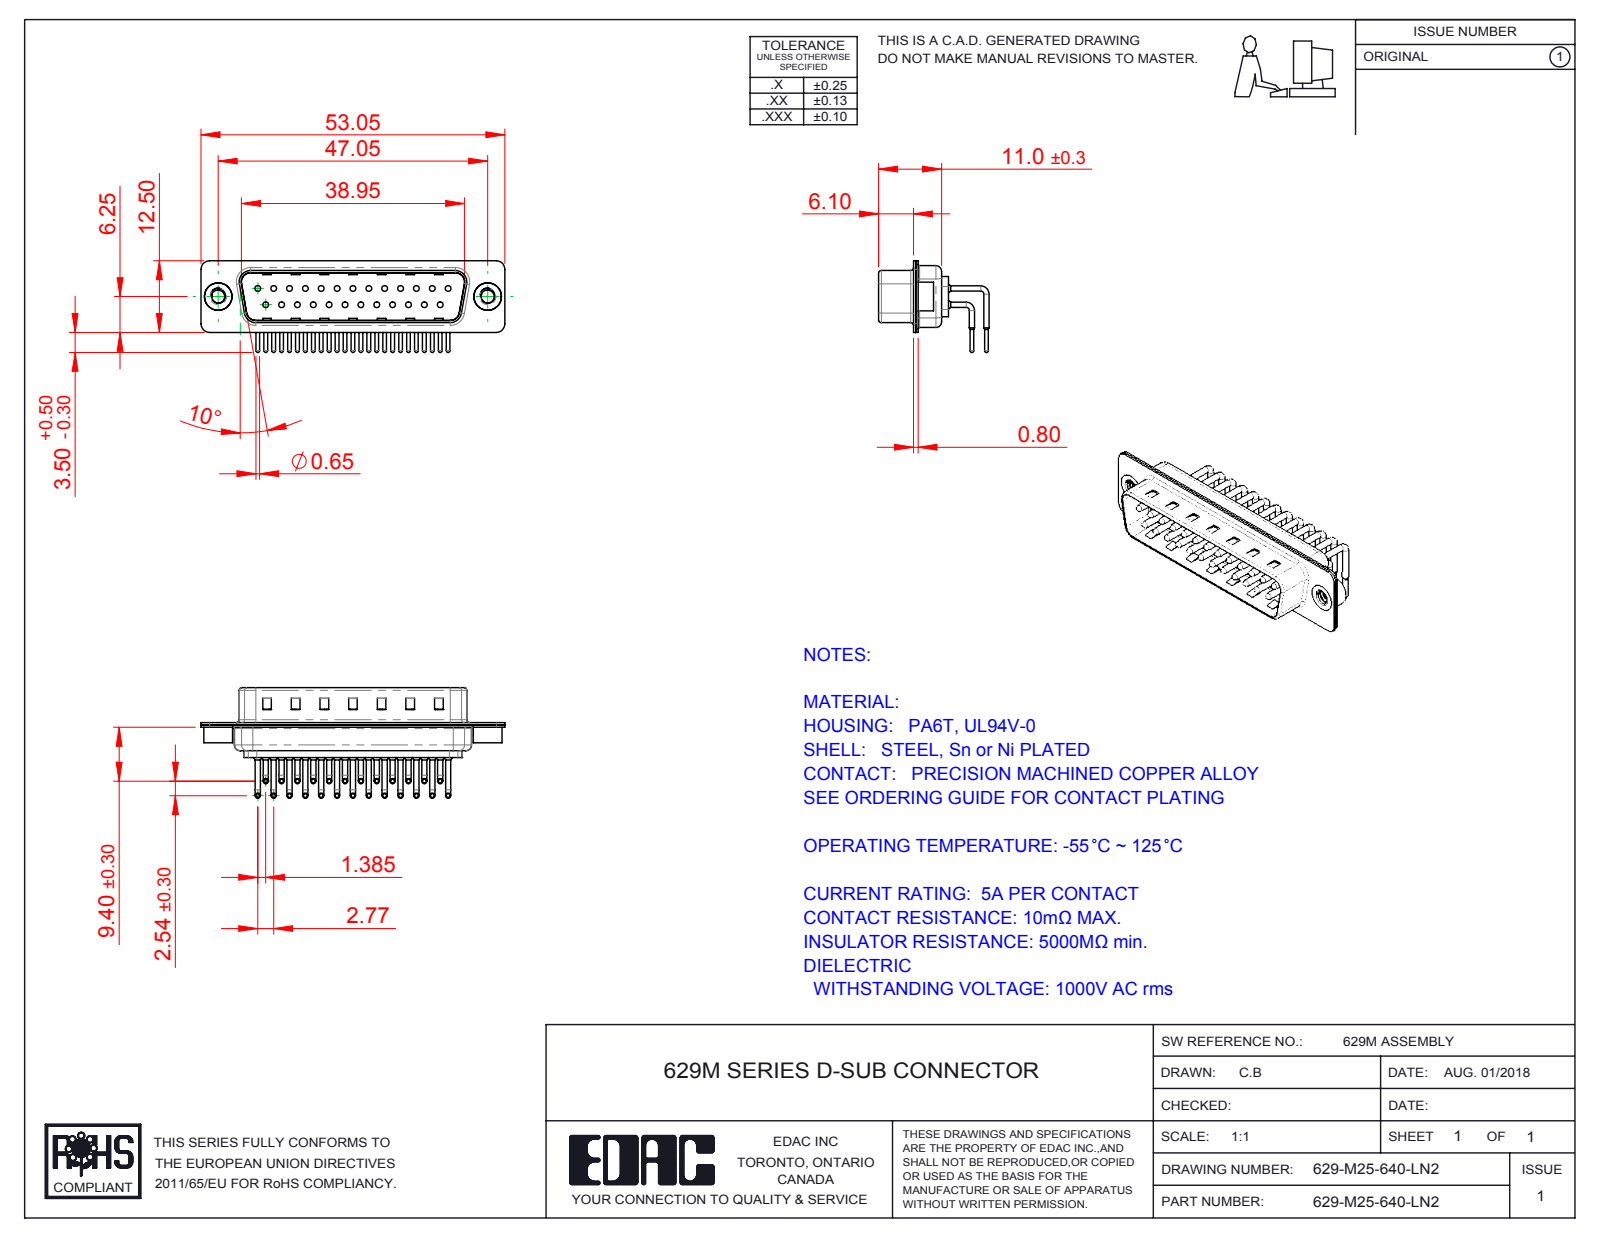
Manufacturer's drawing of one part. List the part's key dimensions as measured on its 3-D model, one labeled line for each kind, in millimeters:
Part name (STEP PRODUCT): 629M Contact Row 1; 629-M25-640-LN2; 629M Shell Front_25 Contacts; 629M 4-40 Threaded Rivet (+3 more)
STEP written by: SolidWorks 2016 (CONFIG_CONTROL_DESIGN)
Units: millimetres
Bodies: 30 solids, 3126 faces (1771 planar, 1037 cylindrical, 318 other)
Overall size (bounding box): 53.05 × 19.29 × 16
Volume: 2 911 mm³ · Surface area: 7 760 mm²
Round holes (diameter × count): ⌀1 ×25, ⌀1.7 ×25, ⌀2 ×25, ⌀2.26 ×2, ⌀4 ×2, ⌀4.8 ×2
Round bosses / shafts (diameter × count): ⌀0.9 ×50, ⌀1.5 ×25, ⌀0.65 ×25, ⌀5 ×2, ⌀4.9 ×2
Partial cylindrical surfaces — rounded edges, fillets, slot ends (radius × count): R1.01 ×25, R1.5 ×16, R2 ×12, R0.5 ×8, R1.6 ×8, R0.25 ×4, R0.6 ×4, R0.65 ×4
Main face-to-face distances: 0.4, 0.85, 9.55, 8.7, 1.25, 10.4, 1.5, 1.9, 0.35, 6.1
Hole centre spacings: 3.16, 2.77, 5.54, 8.31, 11.08, 13.85, 5.04, 7.49
